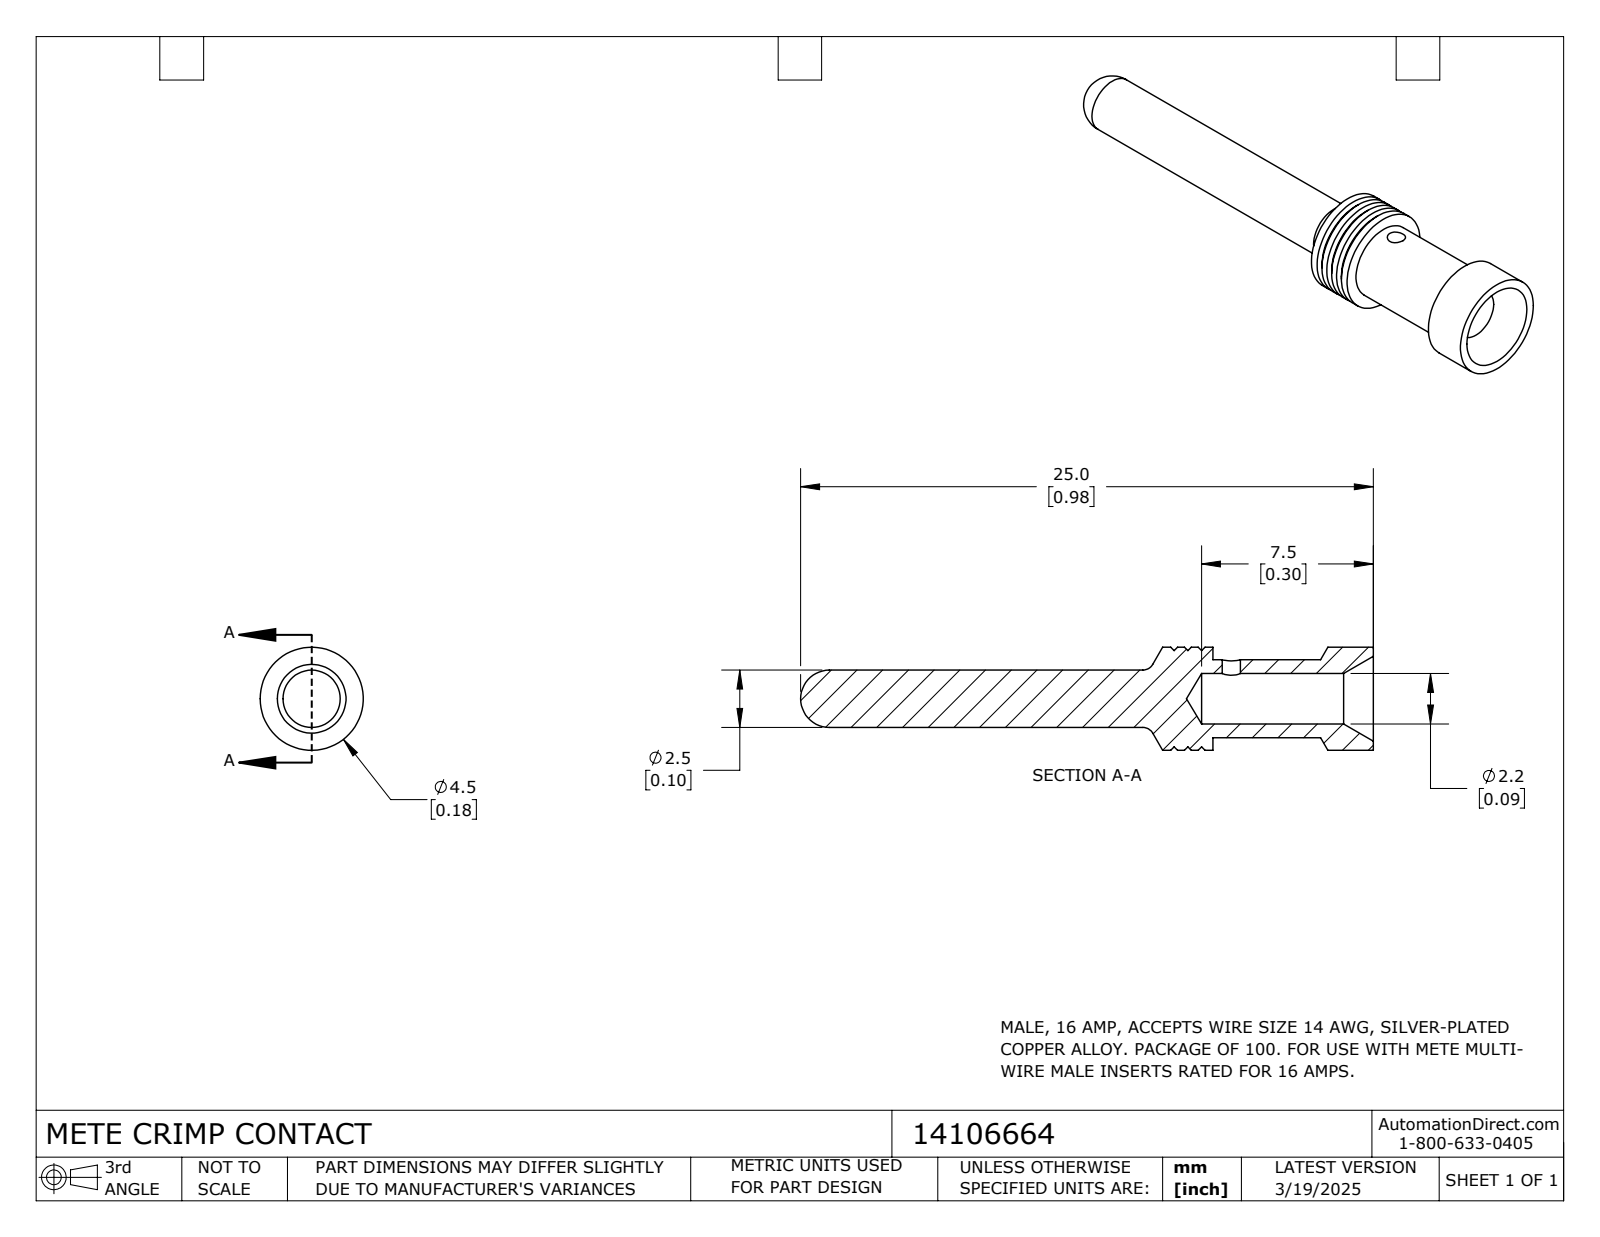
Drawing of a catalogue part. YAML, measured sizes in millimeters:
part_name: "14106664"
step_written_by: "SolidWorks 2024 (CONFIG_CONTROL_DESIGN)"
units: millimeters
bodies: {solids: 1, faces: 44, planar: 2, cylindrical: 18, other: 24}
overall_size: [25, 4.5, 4.5]
volume: 157
surface_area: 327
round_holes:
  - {diameter: 0.8, count: 1}
  - {diameter: 2.2, count: 1}
round_bosses_or_shafts:
  - {diameter: 4.5, count: 1}
  - {diameter: 3.4, count: 1}
  - {diameter: 2.5, count: 1}
face_to_face_distances: [7]
